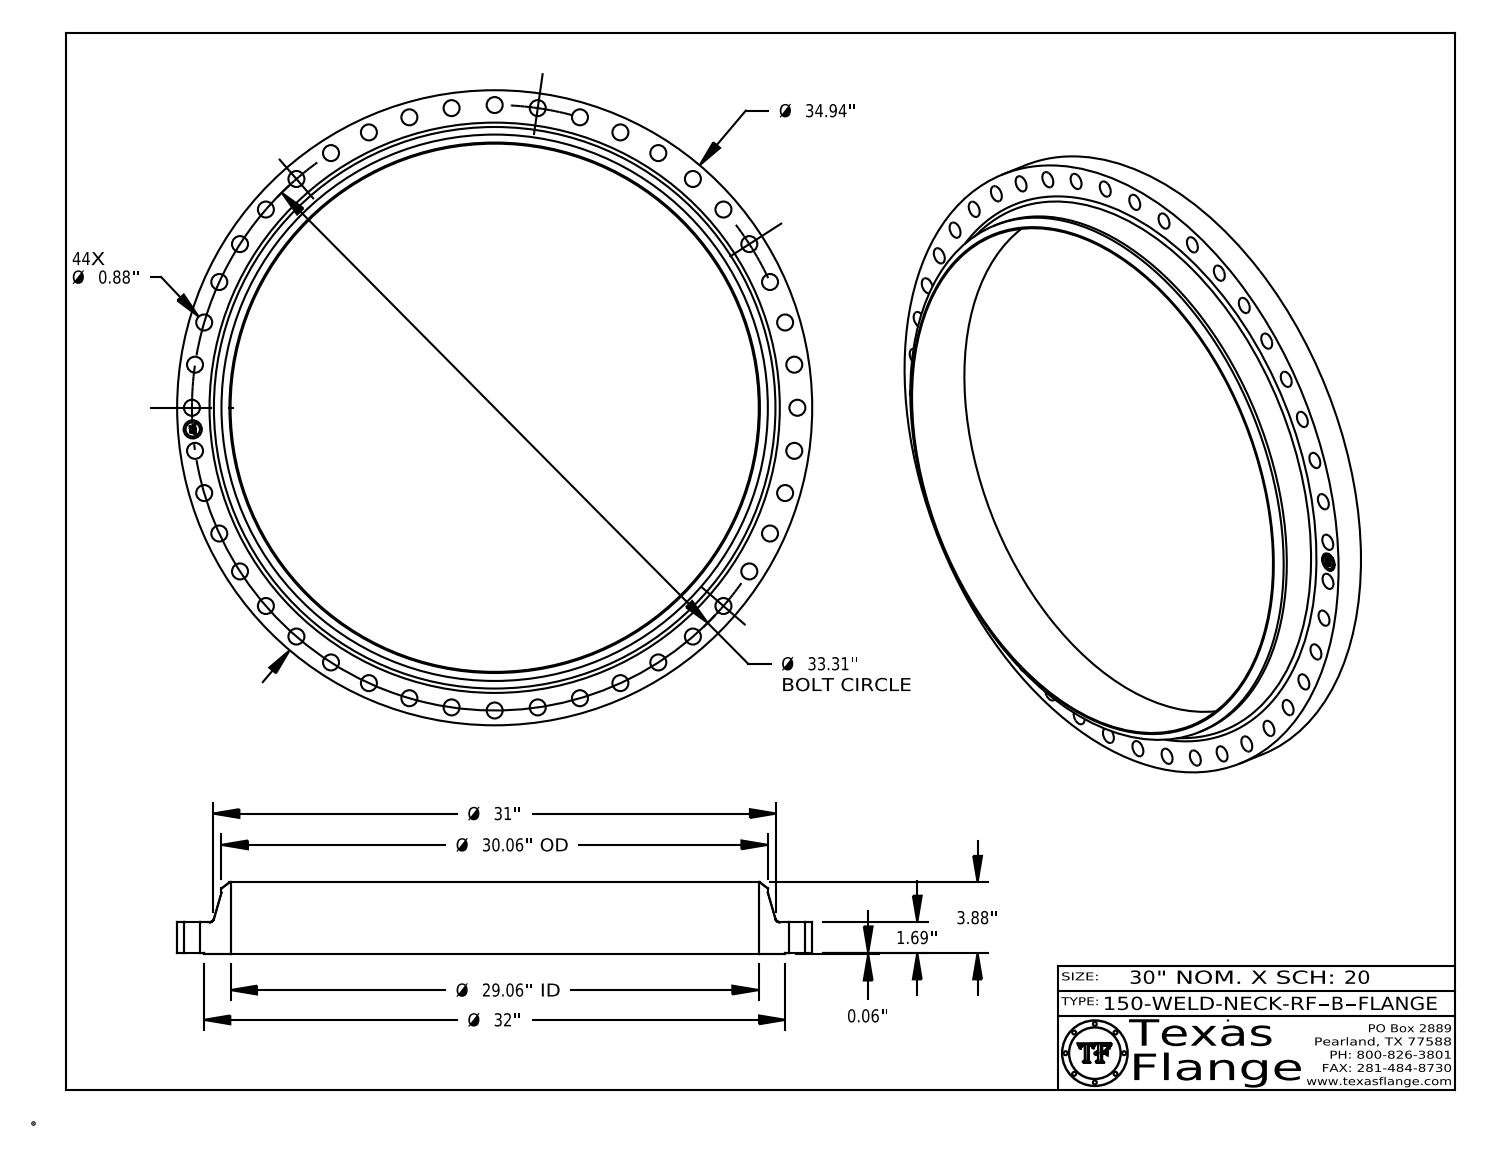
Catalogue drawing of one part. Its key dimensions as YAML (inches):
part_name: "150-WELD-NECK-RF, Series B"
step_written_by: "CATIA V5 STEP AP214 (AUTOMOTIVE_DESIGN)"
units: inches
bodies: {solids: 1, faces: 491, planar: 369, cylindrical: 116, other: 6}
overall_size: [34.94, 34.94, 3.943]
volume: 594.9
surface_area: 1439
round_holes:
  - {diameter: 0.88, count: 44}
  - {diameter: 1, count: 1}
  - {diameter: 29.06, count: 1}
round_bosses_or_shafts:
  - {diameter: 0.061, count: 8}
  - {diameter: 34.94, count: 1}
  - {diameter: 32, count: 1}
  - {diameter: 30.06, count: 1}
  - {diameter: 0.788, count: 1}
face_to_face_distances: [1.753, 0.063, 1.69, 3.943, 3.88, 2.19, 0.015, 1.738, 1.675, 2.205]
hole_center_spacings: [16.655, 2.376, 33.225, 31.961, 32.971, 32.549, 4.741, 11.641]
